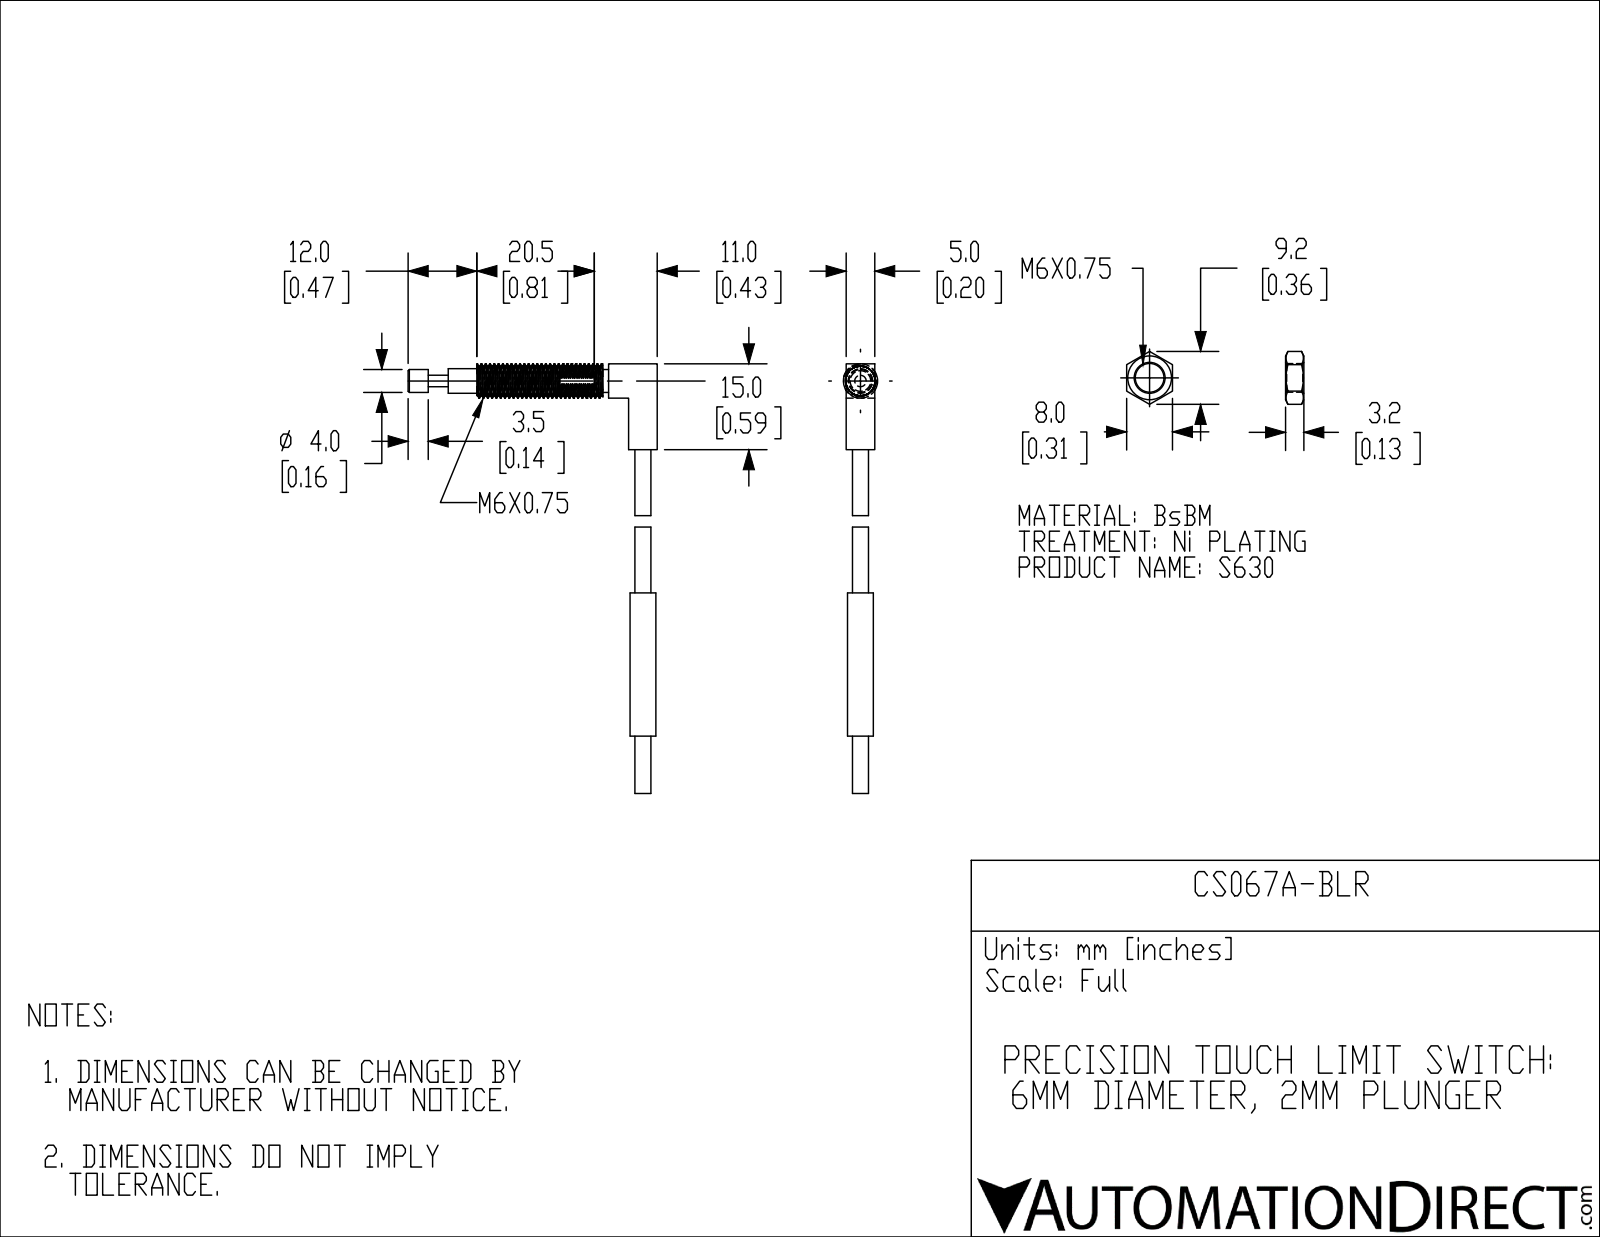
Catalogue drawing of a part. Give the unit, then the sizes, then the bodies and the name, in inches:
Units: inches
Overall size (bounding box): 2.953 × 1.713 × 0.236
Round bosses / shafts (diameter × count): ⌀0.236 ×1, ⌀0.177 ×1, ⌀0.169 ×1, ⌀0.157 ×1, ⌀0.11 ×1, ⌀0.079 ×1
Main face-to-face distances: 0.197, 0.138, 1.24, 0.335, 1.378, 1.043, 0.236, 1.339, 0.984, 1.575
Volume: 0.112 in³ · Surface area: 2.657 in²
Bodies: 2 solids, 34 faces (24 planar, 9 cylindrical, 1 other)
Part name (STEP PRODUCT): CS067A-BLR
STEP written by: SolidWorks 2018 (AUTOMOTIVE_DESIGN)
